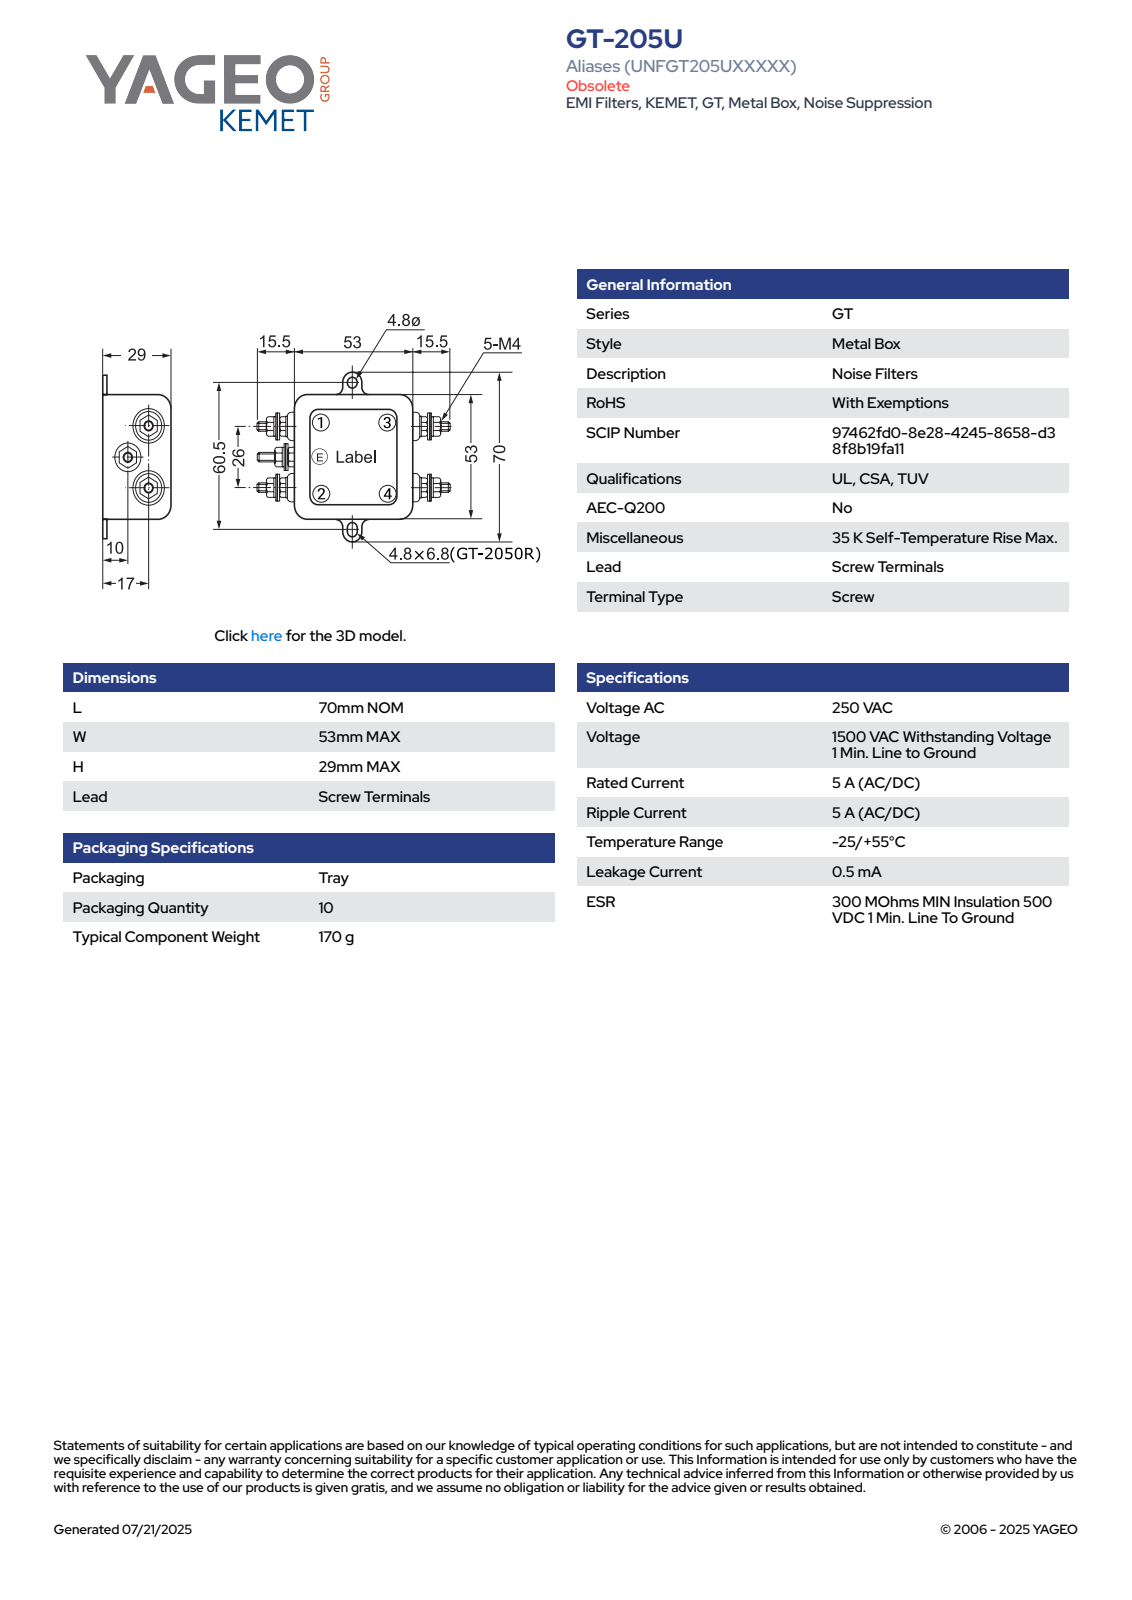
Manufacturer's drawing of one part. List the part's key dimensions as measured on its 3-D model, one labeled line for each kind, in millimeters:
Part name (STEP PRODUCT): Default
STEP written by: SolidWorks 2014 (AUTOMOTIVE_DESIGN)
Units: millimetres
Bodies: 1 solid, 171 faces (83 planar, 66 cylindrical, 22 other)
Overall size (bounding box): 84 × 70 × 29
Volume: 82 696 mm³ · Surface area: 13 001 mm²
Round holes (diameter × count): ⌀4.8 ×1
Round bosses / shafts (diameter × count): ⌀8 ×3, ⌀6 ×3, ⌀4 ×3
Partial cylindrical surfaces — rounded edges, fillets, slot ends (radius × count): R4 ×8, R1 ×4, R2.4 ×2, R4.75 ×2
Main face-to-face distances: 53, 29, 1, 29.01, 28, 28.01, 9, 62, 70, 8
